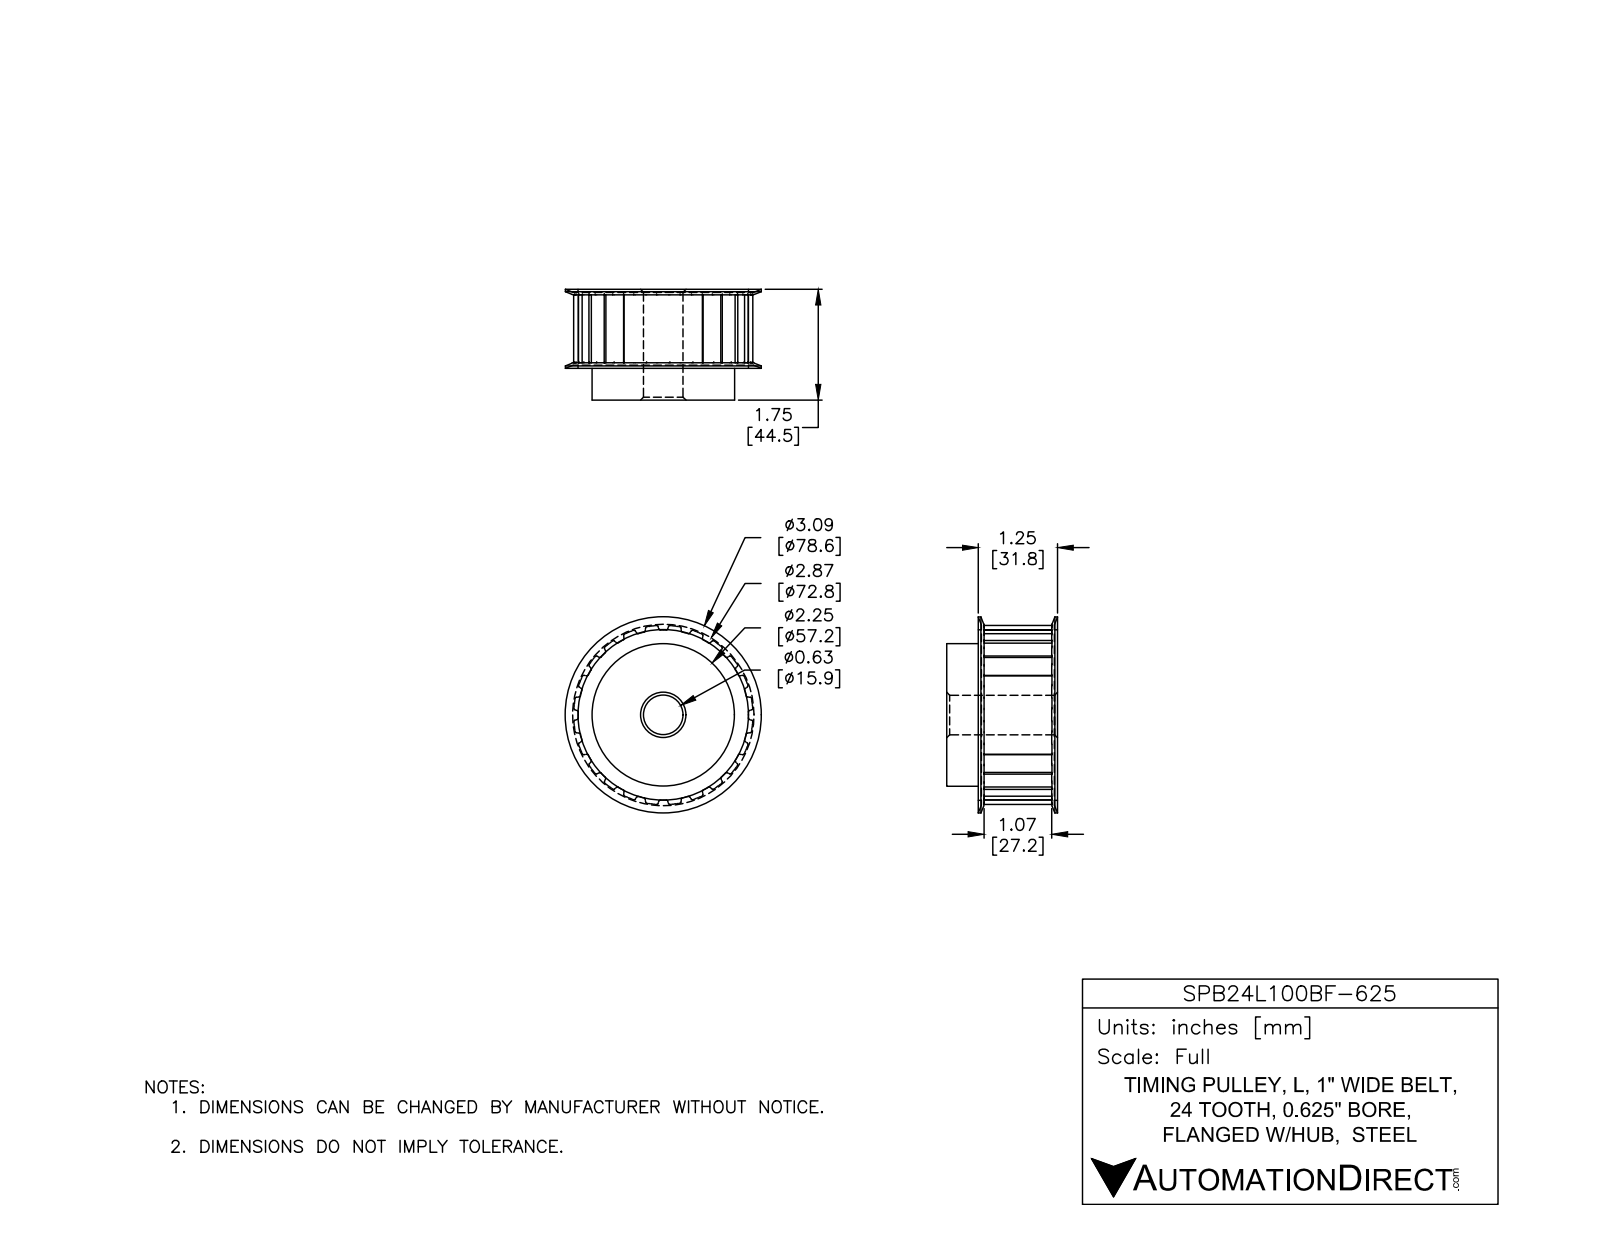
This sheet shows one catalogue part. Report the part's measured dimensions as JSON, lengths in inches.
{"part_name": "SPB24L100BF-625", "step_written_by": "SolidWorks 2015 (AUTOMOTIVE_DESIGN)", "units": "inches", "bodies": {"solids": 1, "faces": 293, "planar": 125, "cylindrical": 152, "other": 16}, "overall_size": [3.094, 3.094, 1.75], "volume_in3": 8.986, "surface_area_in2": 39.55, "round_holes": [[0.625, 1]], "round_bosses_or_shafts": [[3.094, 1], [2.692, 1], [2.25, 1]], "partial_cylinders_radius": [[0.015, 94], [1.309, 1]], "face_to_face_distances": [1.75, 1.25, 0.5, 0.05, 1.2, 0.799, 0.798, 2.834, 2.835, 2.835]}
